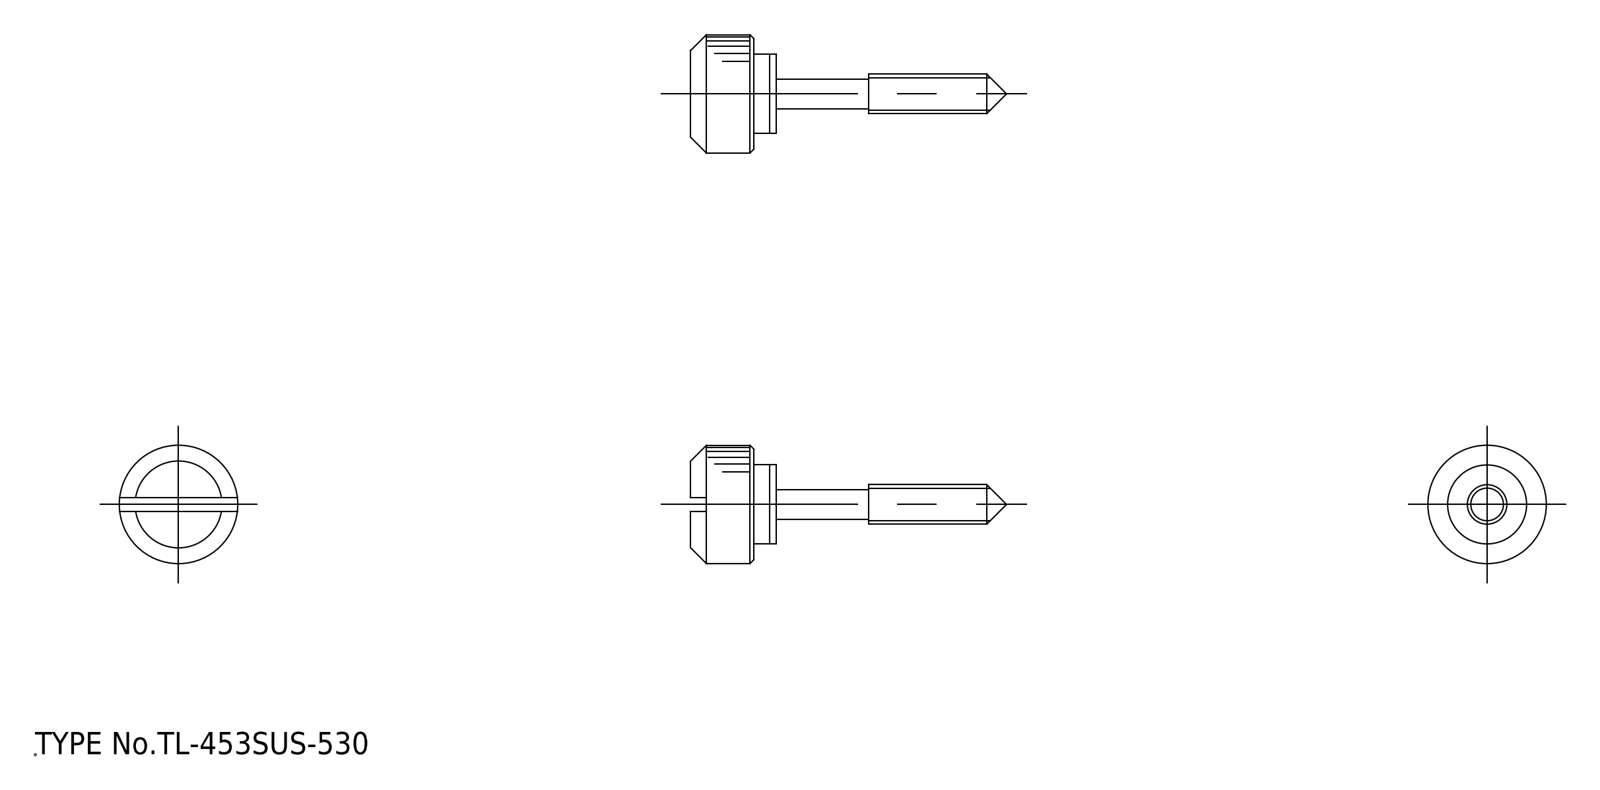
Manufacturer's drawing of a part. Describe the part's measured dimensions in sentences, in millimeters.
The part is named "washer; knob". Its 3-D file was written by "spGate 19.8.4 (****-****-****-****) (AUTOMOTIVE_DESIGN)". It is 2 solids with 42 faces: 18 planar, 18 cylindrical and 6 other. Overall it measures 40 by 15 by 15 millimeters. Its volume is 1 934 cubic millimeters and its surface area 1 339 square millimeters. Round bosses or shafts: 1 of diameter 15, 1 of diameter 10, 1 of diameter 5, 1 of diameter 3.8. Partial cylindrical surfaces (rounded edges, fillets, slot ends): 4 of radius 0.8, 1 of radius 1.95. The main face-to-face distances are 2, 8, 10, 10.8, 2.8, 0.8, 6, 8.8, 1.8, 22.5.
